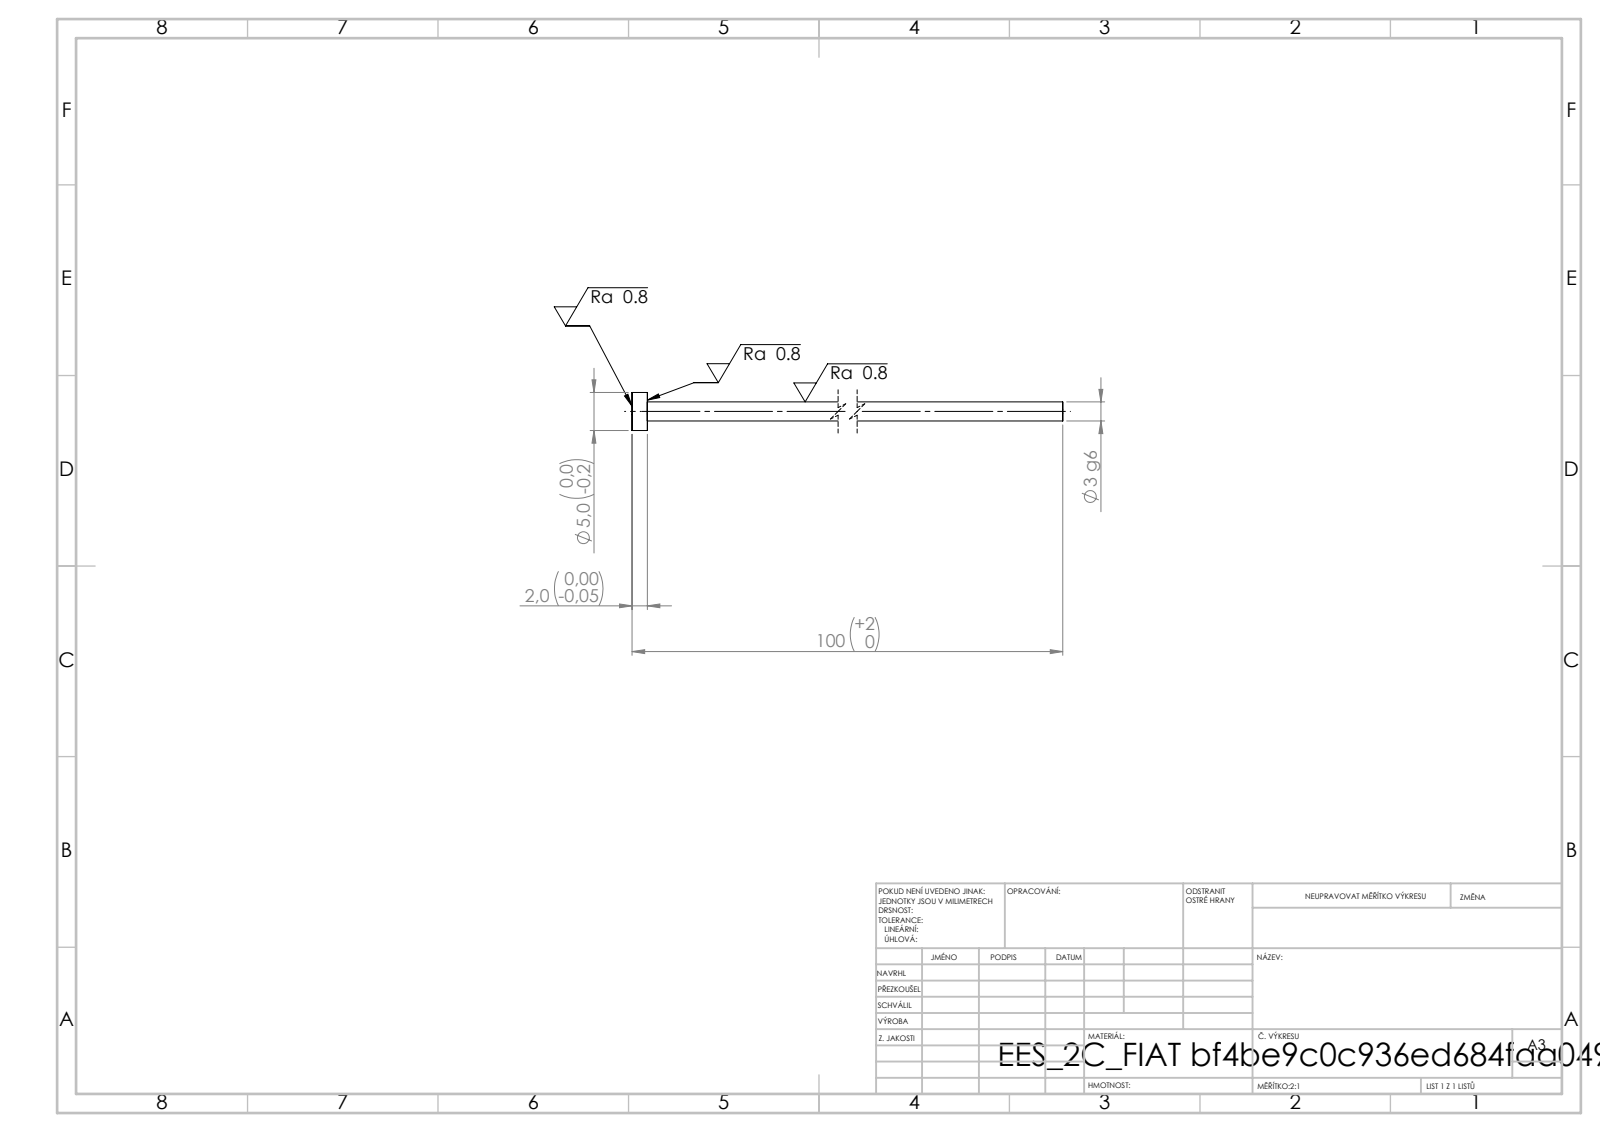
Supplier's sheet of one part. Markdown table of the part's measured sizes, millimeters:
| quantity | value |
| --- | --- |
| STEP written by | SolidWorks 2019 (CONFIG_CONTROL_DESIGN) |
| units | millimeters |
| bodies | 1 solid, 7 faces (3 planar, 4 cylindrical, 0 other) |
| overall size | 100 × 5 × 5 |
| volume | 520 mm³ |
| surface area | 840 mm² |
| round bosses / shafts (diameter × count) | 5 × 1, 2.5 × 1 |
| main face-to-face distances | 2, 100, 98 |
